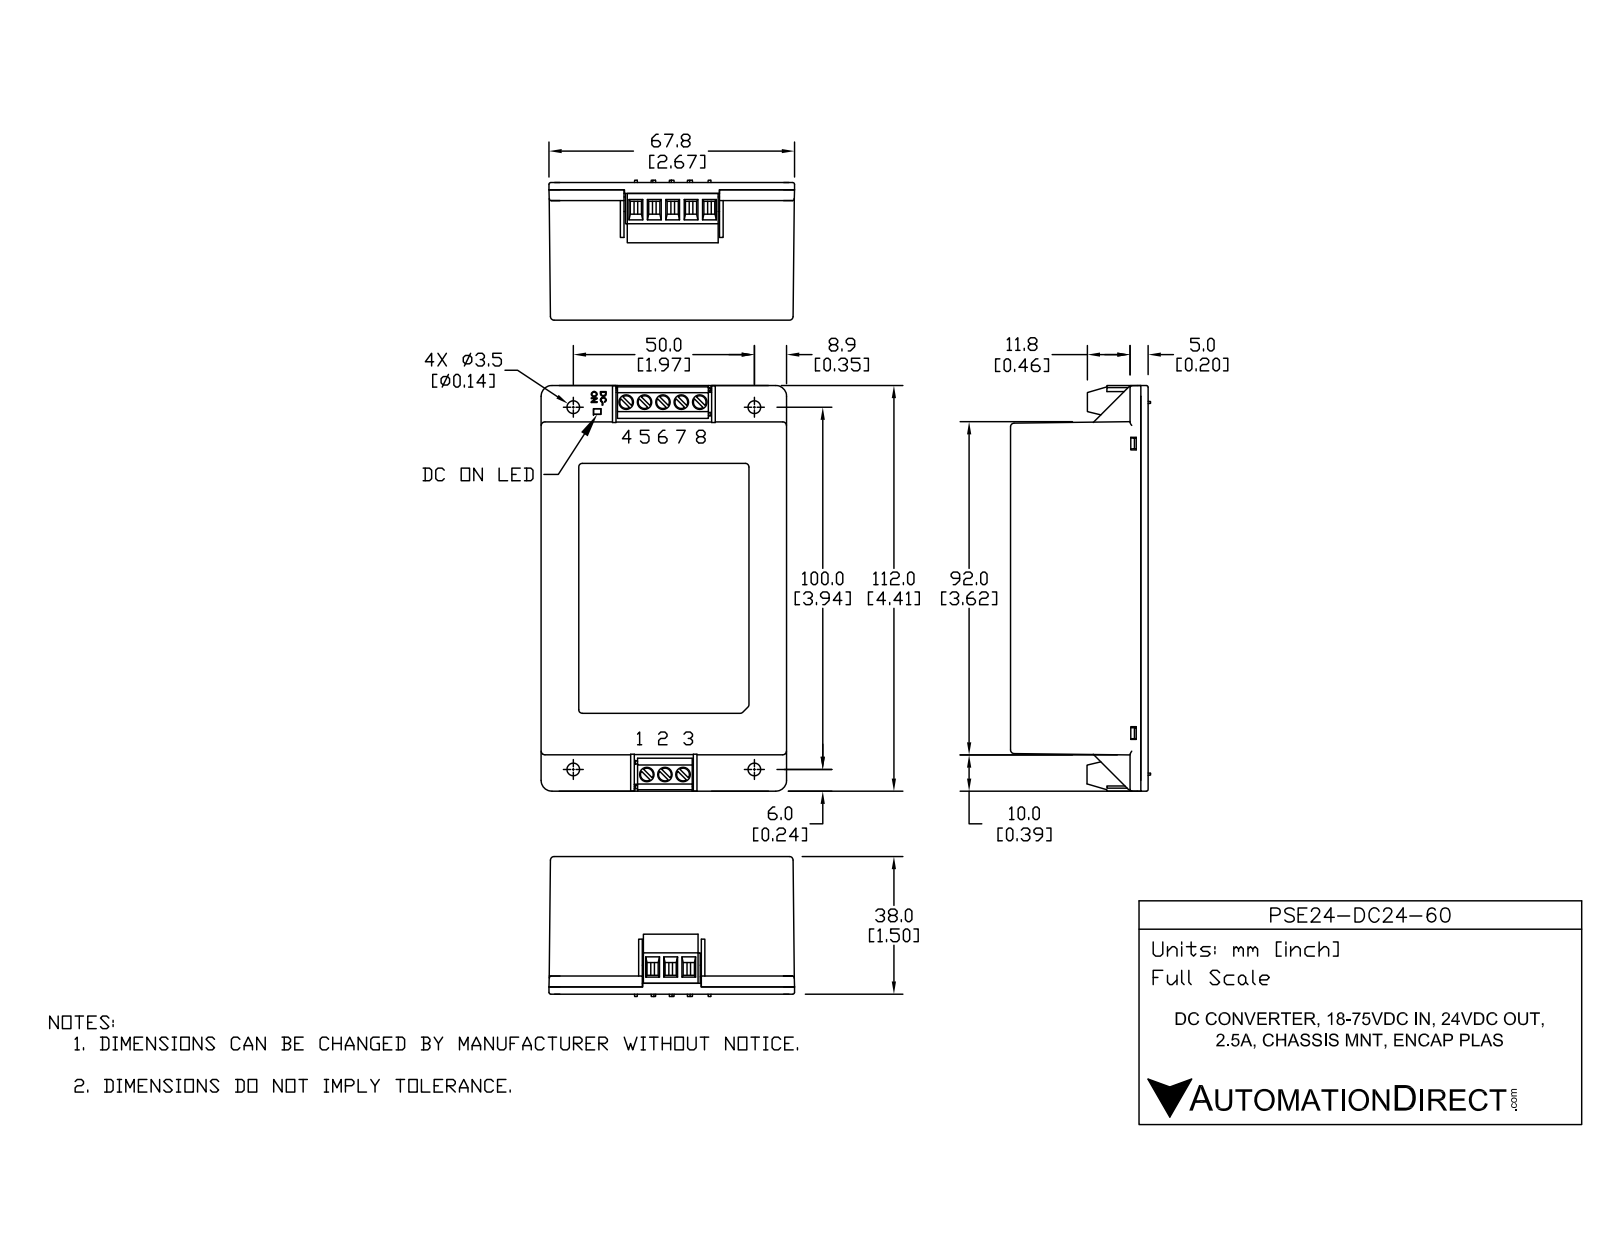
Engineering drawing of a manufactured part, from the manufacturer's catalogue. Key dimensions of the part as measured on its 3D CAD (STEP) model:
Part name (STEP PRODUCT): PSE24-DC24-60
STEP written by: SolidWorks 2015 (AUTOMOTIVE_DESIGN)
Units: millimetres
Bodies: 0 solids, 390 faces (282 planar, 89 cylindrical, 19 other)
Overall size (bounding box): 112.92 × 69.3 × 37.06
Round holes (diameter × count): ⌀4 ×10, ⌀3.5 ×4, ⌀2.46 ×1, ⌀4.08 ×1, ⌀6.5 ×1
Round bosses / shafts (diameter × count): ⌀1.5 ×4, ⌀5 ×1
Partial cylindrical surfaces — rounded edges, fillets, slot ends (radius × count): R1 ×17, R0.5 ×8, R2.15 ×4, R2.65 ×4, R3 ×4, R3.25 ×3
Main face-to-face distances: 1, 0.98, 35, 34, 0.7, 1.02, 1.7, 33.3, 34.99, 33.99
Hole centre spacings: 5.08, 10.16, 50, 102.13, 102.29, 5, 15.24, 100
